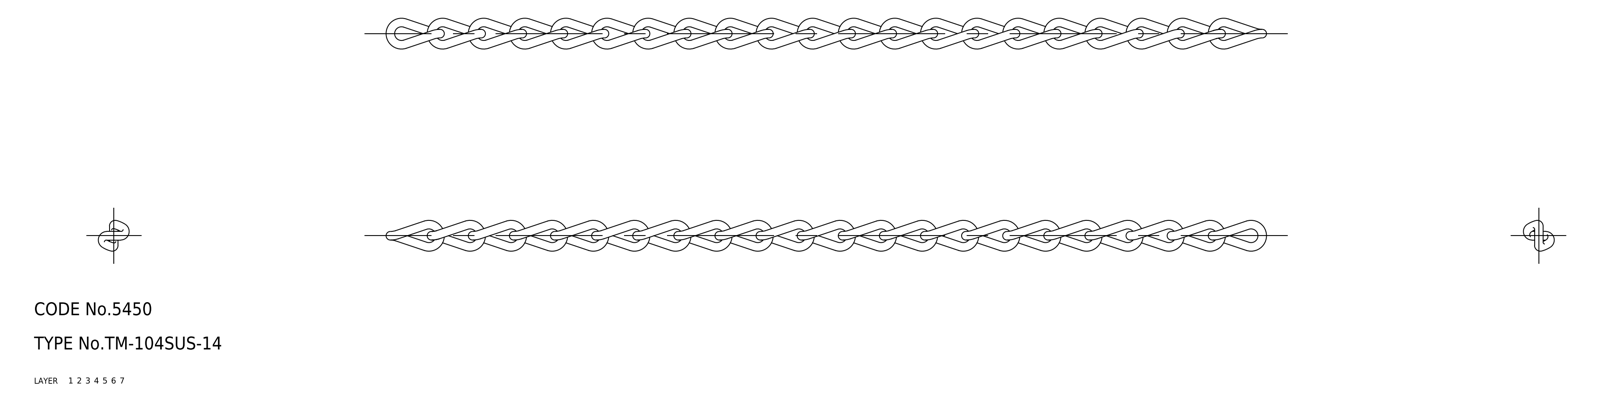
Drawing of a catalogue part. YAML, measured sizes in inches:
part_name: "chain; TM_104SUS_14_10195_36"
step_written_by: "CADfix (AUTOMOTIVE_DESIGN)"
units: inches
bodies: {solids: 21, faces: 504, planar: 0, cylindrical: 0, other: 504}
overall_size: [8.094, 0.283, 0.283]
volume: 0.124
surface_area: 6.282
